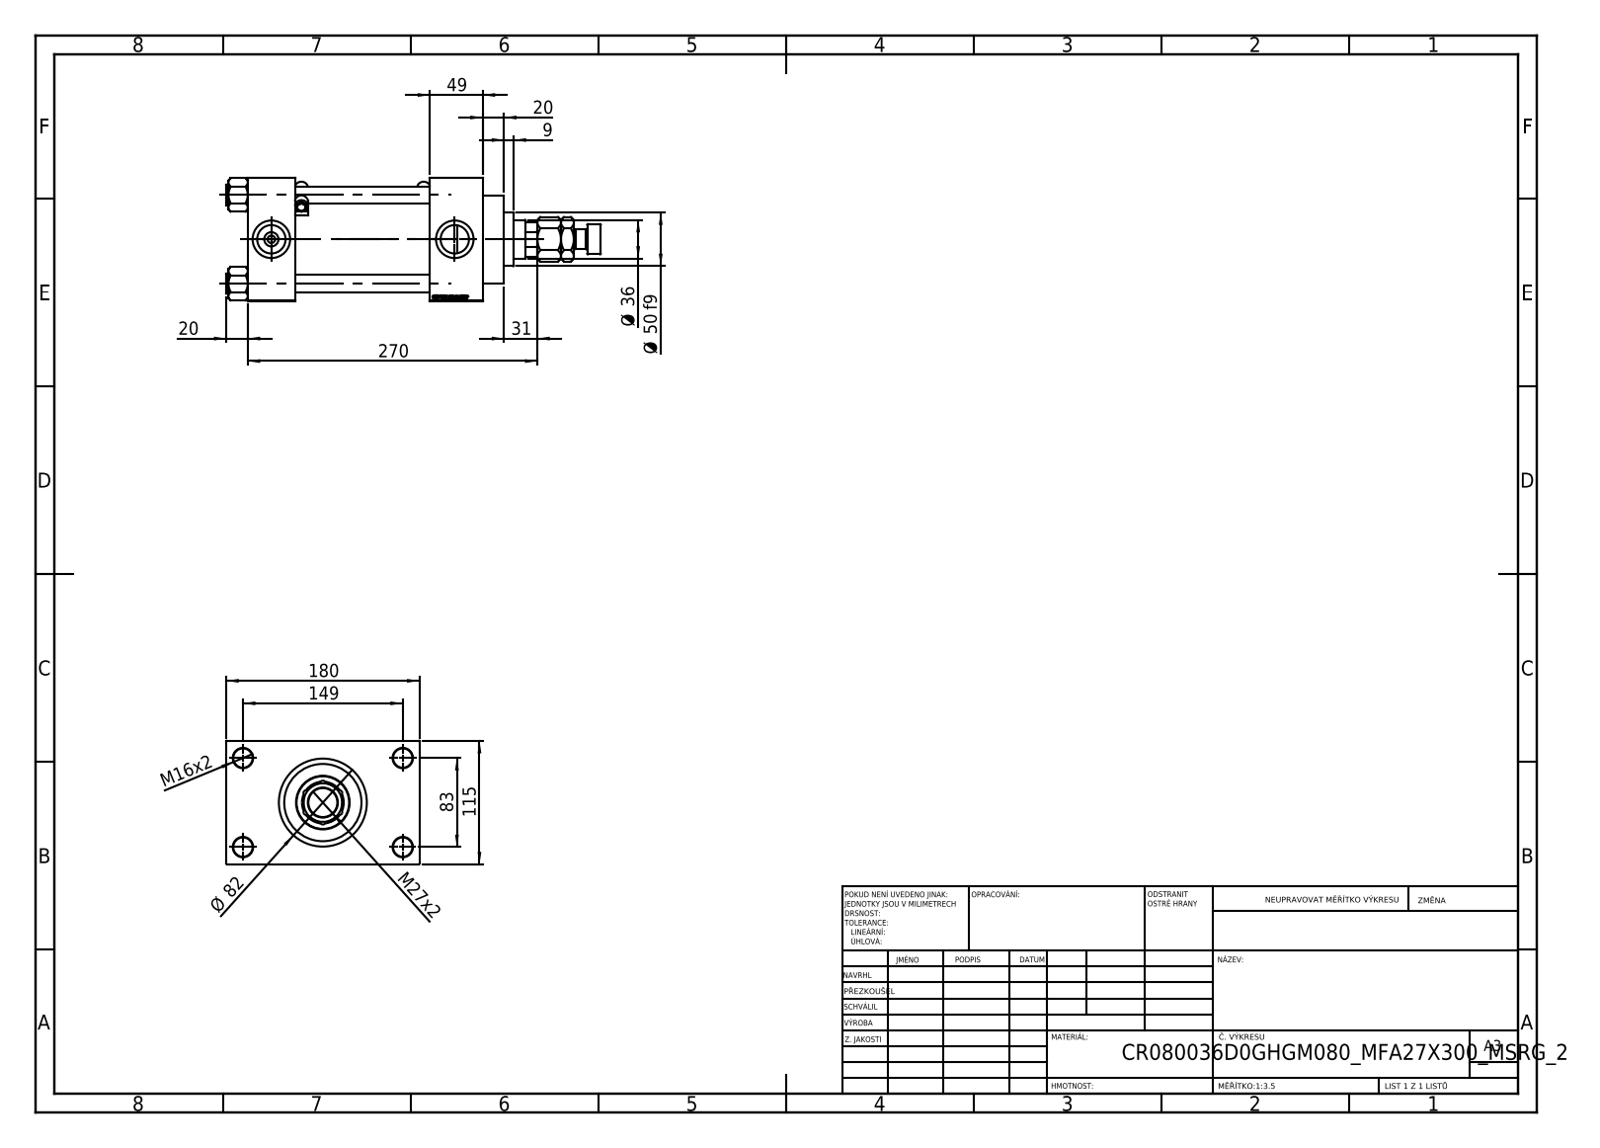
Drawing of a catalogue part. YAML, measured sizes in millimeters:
part_name: "V215CR_VCP_D; V215CR_D_TYCINKA; NUT_M5_D; MFA (+3 more)"
step_written_by: "SolidWorks 2019 (CONFIG_CONTROL_DESIGN)"
units: millimeters
bodies: {solids: 14, faces: 1267, planar: 597, cylindrical: 120, other: 550}
overall_size: [349, 180, 115]
volume: 2192000
surface_area: 360239
round_holes:
  - {diameter: 16, count: 4}
  - {diameter: 18, count: 4}
  - {diameter: 7, count: 2}
  - {diameter: 26.44, count: 2}
  - {diameter: 35, count: 2}
  - {diameter: 25.5, count: 1}
  - {diameter: 36, count: 1}
  - {diameter: 39, count: 1}
  - {diameter: 61, count: 1}
  - {diameter: 72, count: 1}
  - {diameter: 80, count: 1}
round_bosses_or_shafts:
  - {diameter: 19, count: 4}
  - {diameter: 5, count: 2}
  - {diameter: 2.5, count: 2}
  - {diameter: 86, count: 1}
  - {diameter: 82, count: 1}
  - {diameter: 50, count: 1}
  - {diameter: 28, count: 1}
  - {diameter: 18, count: 1}
partial_cylinders:
  - {radius: 0.5, count: 12}
  - {radius: 6, count: 4}
  - {radius: 17.5, count: 1}
face_to_face_distances: [115, 126, 175, 49, 170, 44, 219, 32.5, 147.5, 180]
hole_center_spacings: [33.15, 58.48, 82.7, 85.28, 89.24, 115.85, 142.43, 83]
